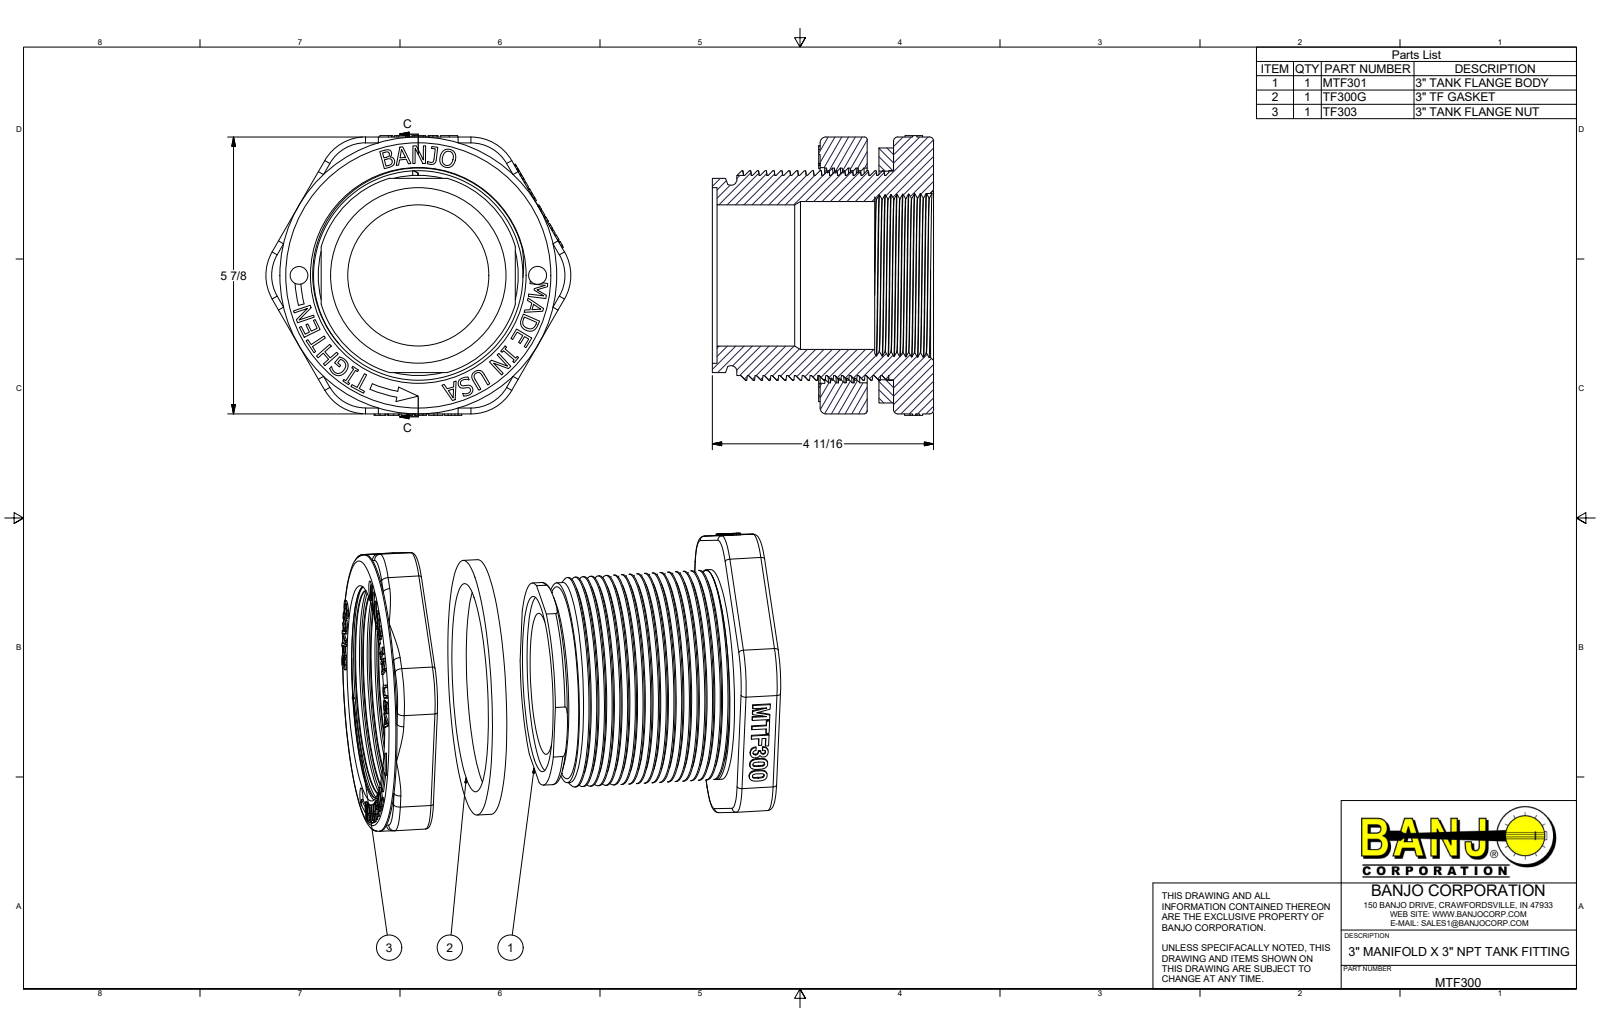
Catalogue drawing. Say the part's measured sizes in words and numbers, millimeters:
The part is named "MTF300; MTF301; TF300G; TF303 (+1 more)". Its 3-D file was written by "Autodesk Inventor 2017 (AUTOMOTIVE_DESIGN)". It is 3 solids with 858 faces: 495 planar, 90 cylindrical and 273 other. Overall it measures 164.6 by 150.93 by 119.38 millimeters. Its volume is 976 785 cubic millimeters and its surface area 193 639 square millimeters. Round holes: 2 of diameter 9.65, 1 of diameter 76.2, 1 of diameter 79.76, 1 of diameter 94.74, 1 of diameter 110.77, 1 of diameter 112.52, 1 of diameter 115.85, 1 of diameter 116.33. Round bosses or shafts: 1 of diameter 149.35, 1 of diameter 137.57, 1 of diameter 113.28, 1 of diameter 113.03, 1 of diameter 107.95. Partial cylindrical surfaces (rounded edges, fillets, slot ends): 12 of radius 2.29, 6 of radius 1.59, 6 of radius 3.17, 6 of radius 25.4, 1 of radius 0.25, 1 of radius 31.5, 1 of radius 54.61, 1 of radius 63.5. The main face-to-face distances are 21.59, 35.81, 14.22, 29.46, 31.75, 7.87, 6.35, 25.4, 39.62, 61.21. The hole center spacings are 64.39, 128.78.
